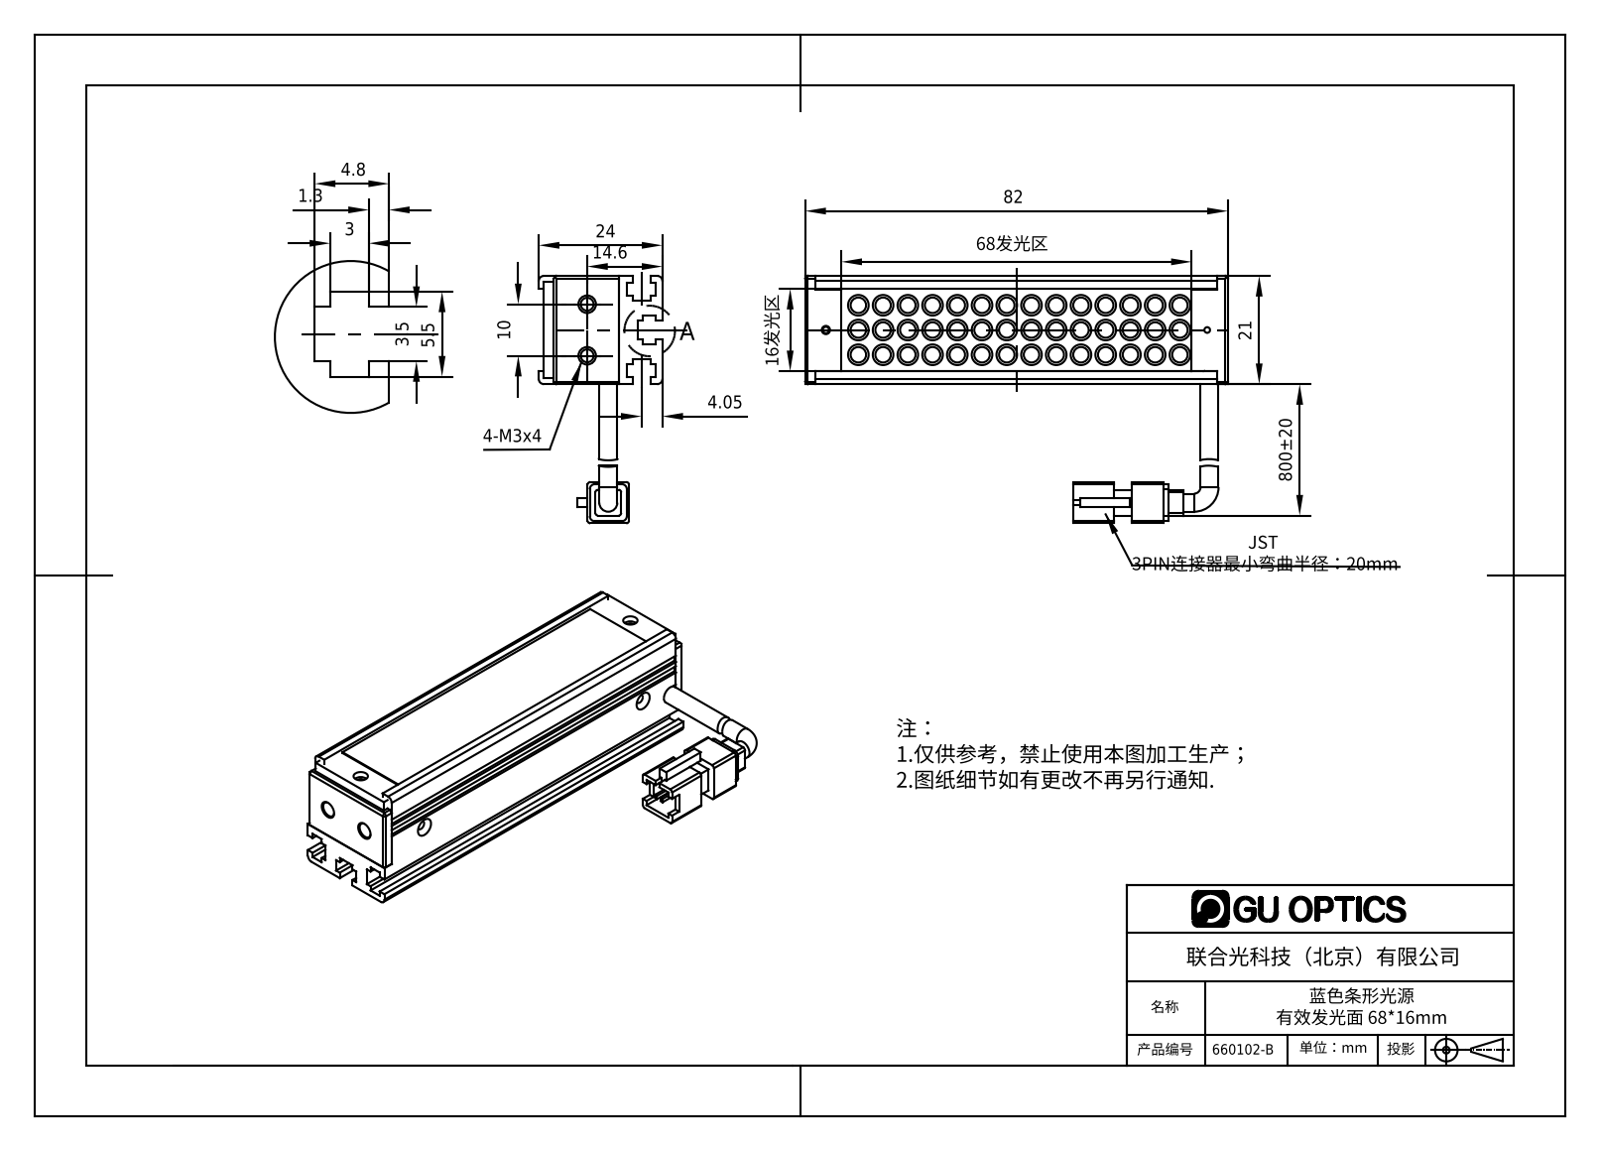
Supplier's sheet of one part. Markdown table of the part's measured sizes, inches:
| quantity | value |
| --- | --- |
| part name | 660102-B |
| STEP written by | SolidWorks 2016 (AUTOMOTIVE_DESIGN) |
| units | inches |
| bodies | 8 solids, 690 faces (294 planar, 251 cylindrical, 145 other) |
| overall size | 3.228 × 1.89 × 0.945 |
| volume | 1.532 in³ |
| surface area | 42.94 in² |
| round holes (diameter × count) | 0.063 × 5, 0.059 × 2, 0.067 × 2, 0.098 × 2, 0.11 × 2, 0.118 × 2, 0.043 × 1, 0.049 × 1, 0.079 × 1 |
| round bosses / shafts (diameter × count) | 0.157 × 42, 0.118 × 42, 0.138 × 2 |
| partial cylindrical surfaces (radius × count) | 0.039 × 12, 0.02 × 8, 0.065 × 1 |
| main face-to-face distances | 0.079, 0.039, 0.098, 0.728, 0.575, 0.827, 0.051, 0.335, 0.138, 0.496 |
| hole center spacings | 2.913, 0.276, 0.283, 0.348, 2.639, 2.646, 2.926, 0.394 |
